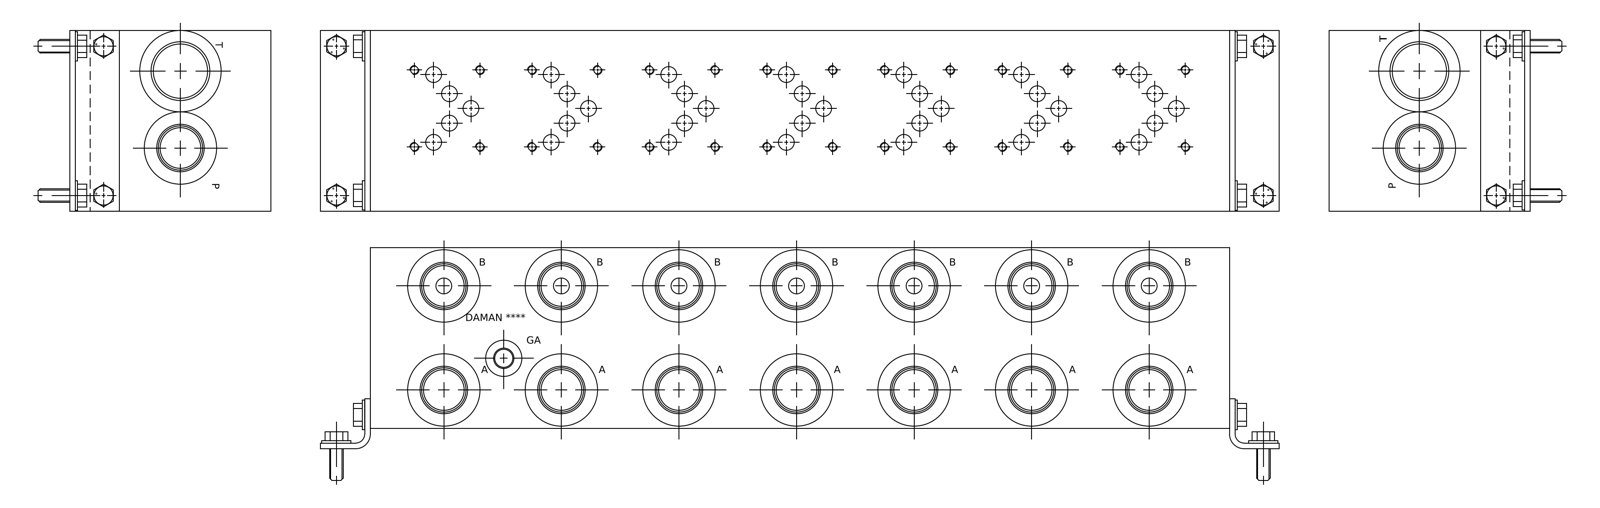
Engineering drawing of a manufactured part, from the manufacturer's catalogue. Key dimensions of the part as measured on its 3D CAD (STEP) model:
Part name (STEP PRODUCT): Part_AD05JP073S_3D
STEP written by: Autodesk Inventor 2020 (AUTOMOTIVE_DESIGN)
Units: millimetres
Bodies: 1 solid, 1136 faces (531 planar, 207 cylindrical, 398 other)
Overall size (bounding box): 603.25 × 127 × 127
Volume: 9 101 000 mm³ · Surface area: 428 852 mm²
Round holes (diameter × count): ⌀5.11 ×28, ⌀6.35 ×28, ⌀31.27 ×15, ⌀33.34 ×15, ⌀33.76 ×15, ⌀48.97 ×15, ⌀10.31 ×14, ⌀11.13 ×14, ⌀28.57 ×14, ⌀35.51 ×13, ⌀9.53 ×9, ⌀7.92 ×2
Main face-to-face distances: 127, 0.79, 126.21, 603.25, 602.46, 19.05, 601.67, 19.84, 107.16, 583.41
Hole centre spacings: 82.55, 165.1, 247.65, 330.2, 95.3, 180.53, 412.75, 35.4
